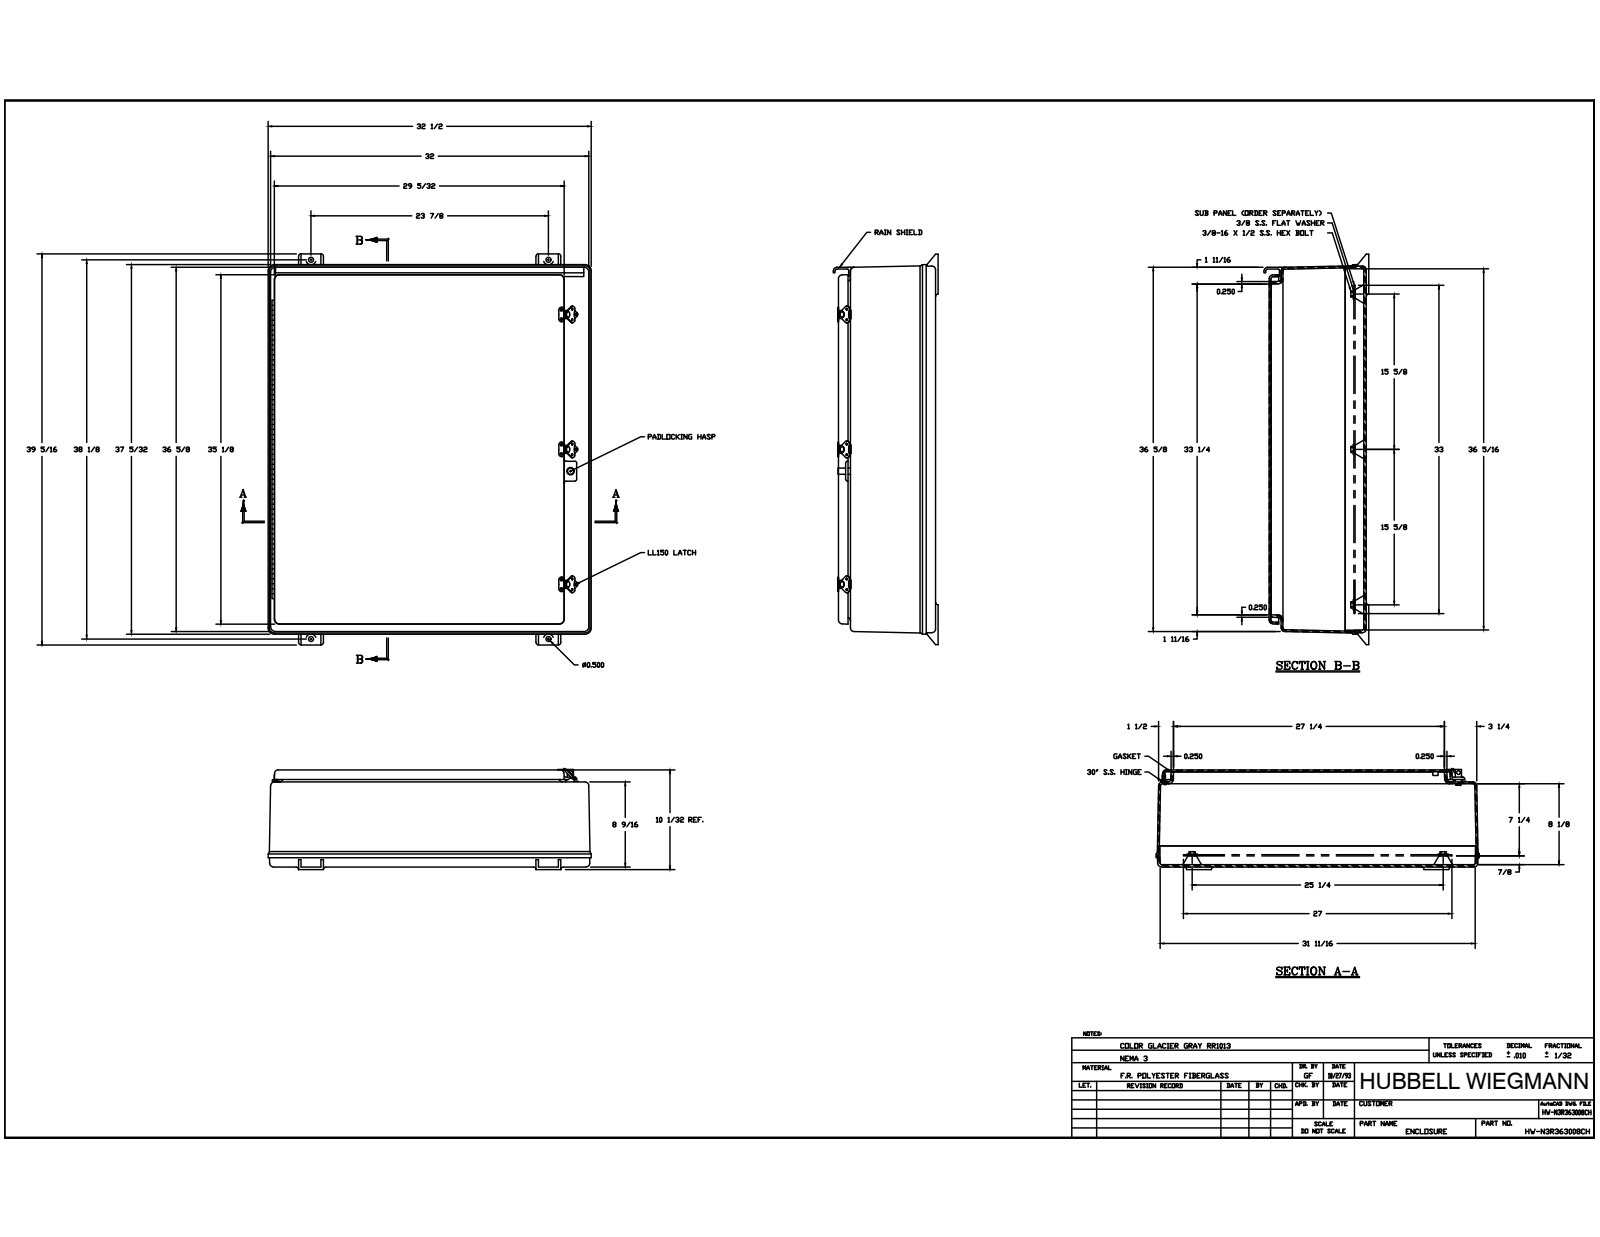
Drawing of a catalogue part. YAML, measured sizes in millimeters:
part_name: "WPN36308SRT; WPN3630B; WPN36308RTPCVR; N36308G (+8 more)"
step_written_by: "Autodesk Inventor 2014 (AUTOMOTIVE_DESIGN)"
units: millimeters
bodies: {solids: 49, faces: 1497, planar: 592, cylindrical: 594, other: 311}
overall_size: [998.54, 825.5, 268.29]
volume: 13750000
surface_area: 5442000
round_holes:
  - {diameter: 3.3, count: 27}
  - {diameter: 1.59, count: 12}
  - {diameter: 1.65, count: 11}
  - {diameter: 3.5, count: 6}
  - {diameter: 4.76, count: 6}
  - {diameter: 14.3, count: 4}
  - {diameter: 11, count: 2}
  - {diameter: 12.95, count: 2}
  - {diameter: 12.96, count: 2}
  - {diameter: 3.17, count: 1}
  - {diameter: 3.43, count: 1}
  - {diameter: 3.97, count: 1}
round_bosses_or_shafts:
  - {diameter: 3.56, count: 12}
  - {diameter: 7.54, count: 11}
  - {diameter: 12.7, count: 3}
  - {diameter: 6.35, count: 1}
  - {diameter: 5.11, count: 1}
  - {diameter: 5.08, count: 1}
partial_cylinders:
  - {radius: 0.25, count: 86}
  - {radius: 4.76, count: 26}
  - {radius: 6.35, count: 24}
  - {radius: 7.94, count: 17}
  - {radius: 9.53, count: 17}
  - {radius: 0.76, count: 12}
  - {radius: 12.7, count: 12}
  - {radius: 2.54, count: 7}
face_to_face_distances: [6.35, 4.78, 248.45, 242.1, 243.67, 237.32, 4.76, 4.77, 217.49, 212.73]
hole_center_spacings: [344.49, 241.3, 495.3, 688.98, 88.25, 345.02, 396.88, 483.71]
